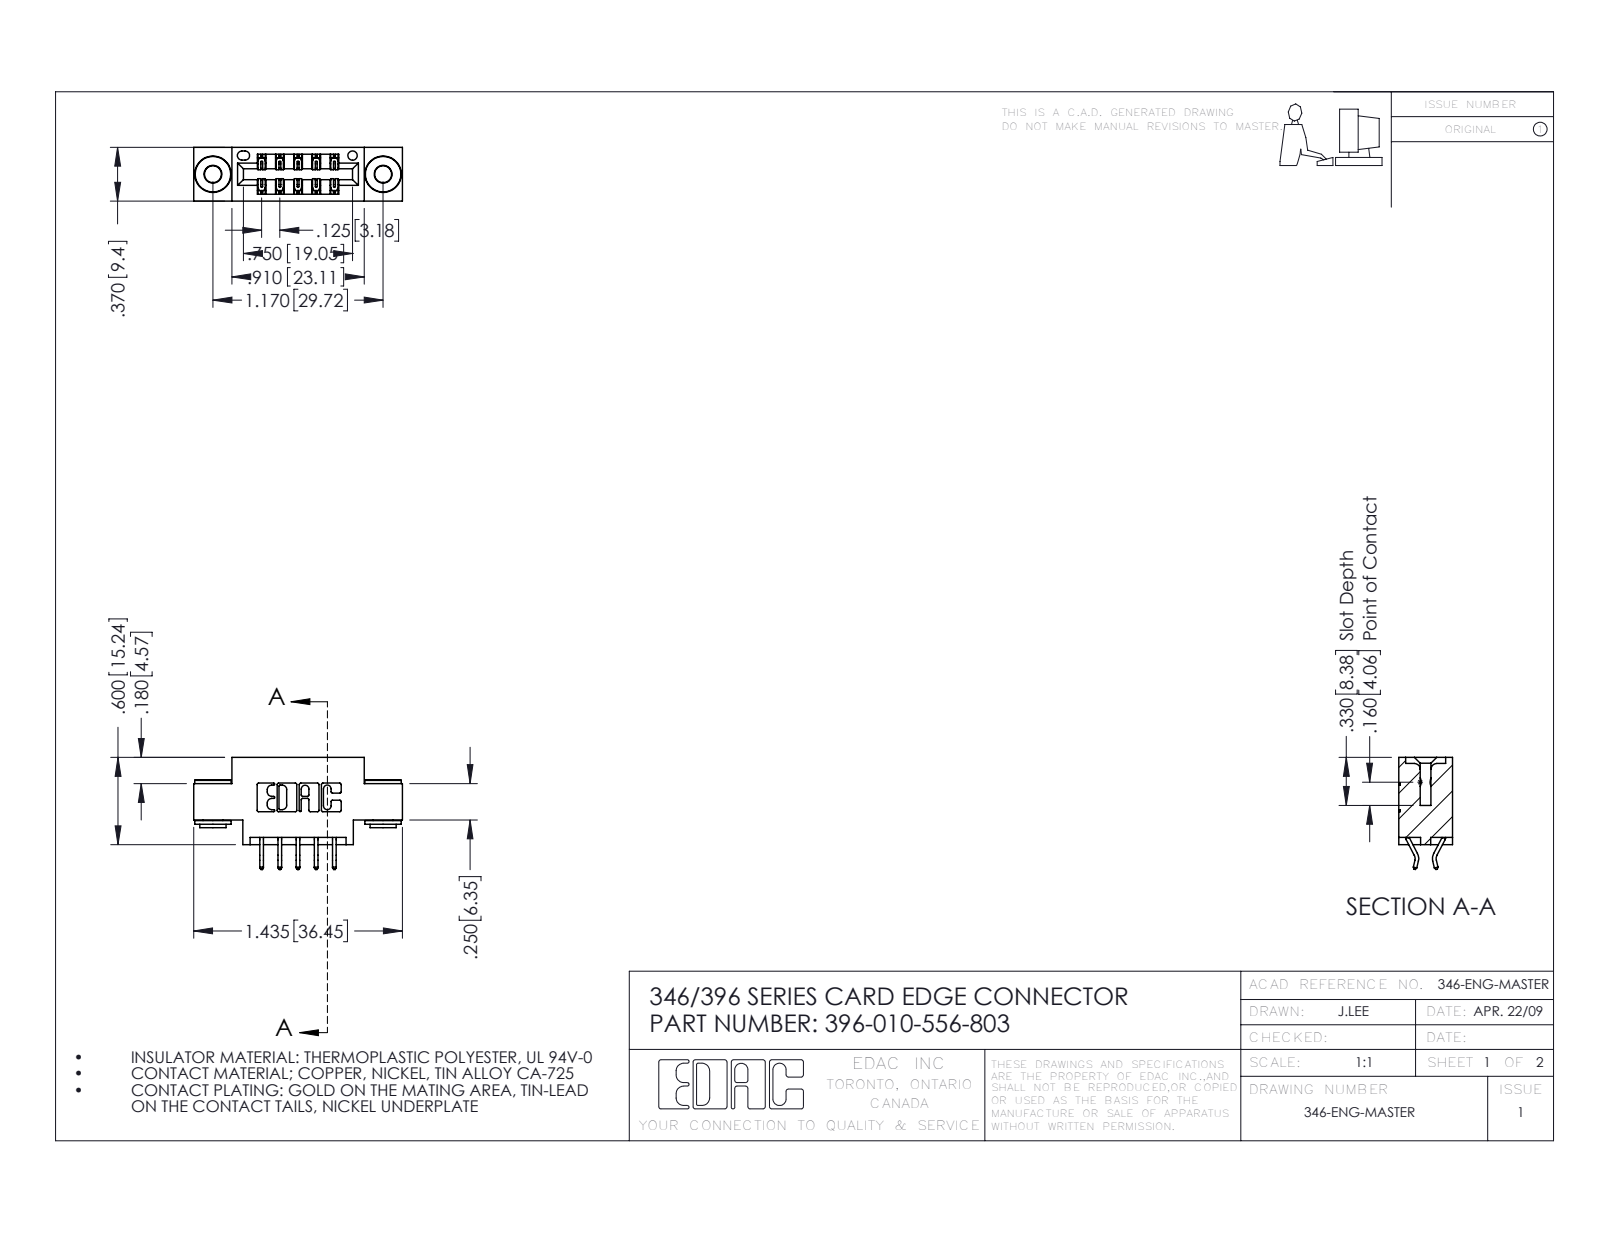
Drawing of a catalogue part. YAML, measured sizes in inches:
part_name: "396-010-556-803; 346 Part_0.170 Offset - 0.156 Dia-TH; 345-250-002_345-250-002-102; 345-292-001_556 Tail"
step_written_by: "SolidWorks 2016 (CONFIG_CONTROL_DESIGN)"
units: inches
bodies: {solids: 13, faces: 744, planar: 480, cylindrical: 256, other: 8}
overall_size: [1.435, 0.77, 0.37]
volume: 0.191
surface_area: 6.366
round_holes:
  - {diameter: 0.116, count: 2}
  - {diameter: 0.156, count: 2}
  - {diameter: 0.064, count: 1}
round_bosses_or_shafts:
  - {diameter: 0.25, count: 2}
  - {diameter: 0.18, count: 2}
  - {diameter: 0.136, count: 2}
partial_cylinders:
  - {radius: 0.01, count: 22}
  - {radius: 0.006, count: 15}
  - {radius: 0.007, count: 6}
  - {radius: 0.031, count: 6}
  - {radius: 0.026, count: 3}
  - {radius: 0.01, count: 2}
  - {radius: 0.014, count: 2}
  - {radius: 0.022, count: 2}
face_to_face_distances: [0.25, 0.37, 0.048, 0.322, 0.025, 0.275, 0.148, 0.222, 0.1, 0.174]
hole_center_spacings: [0.246, 0.969, 1.17]
